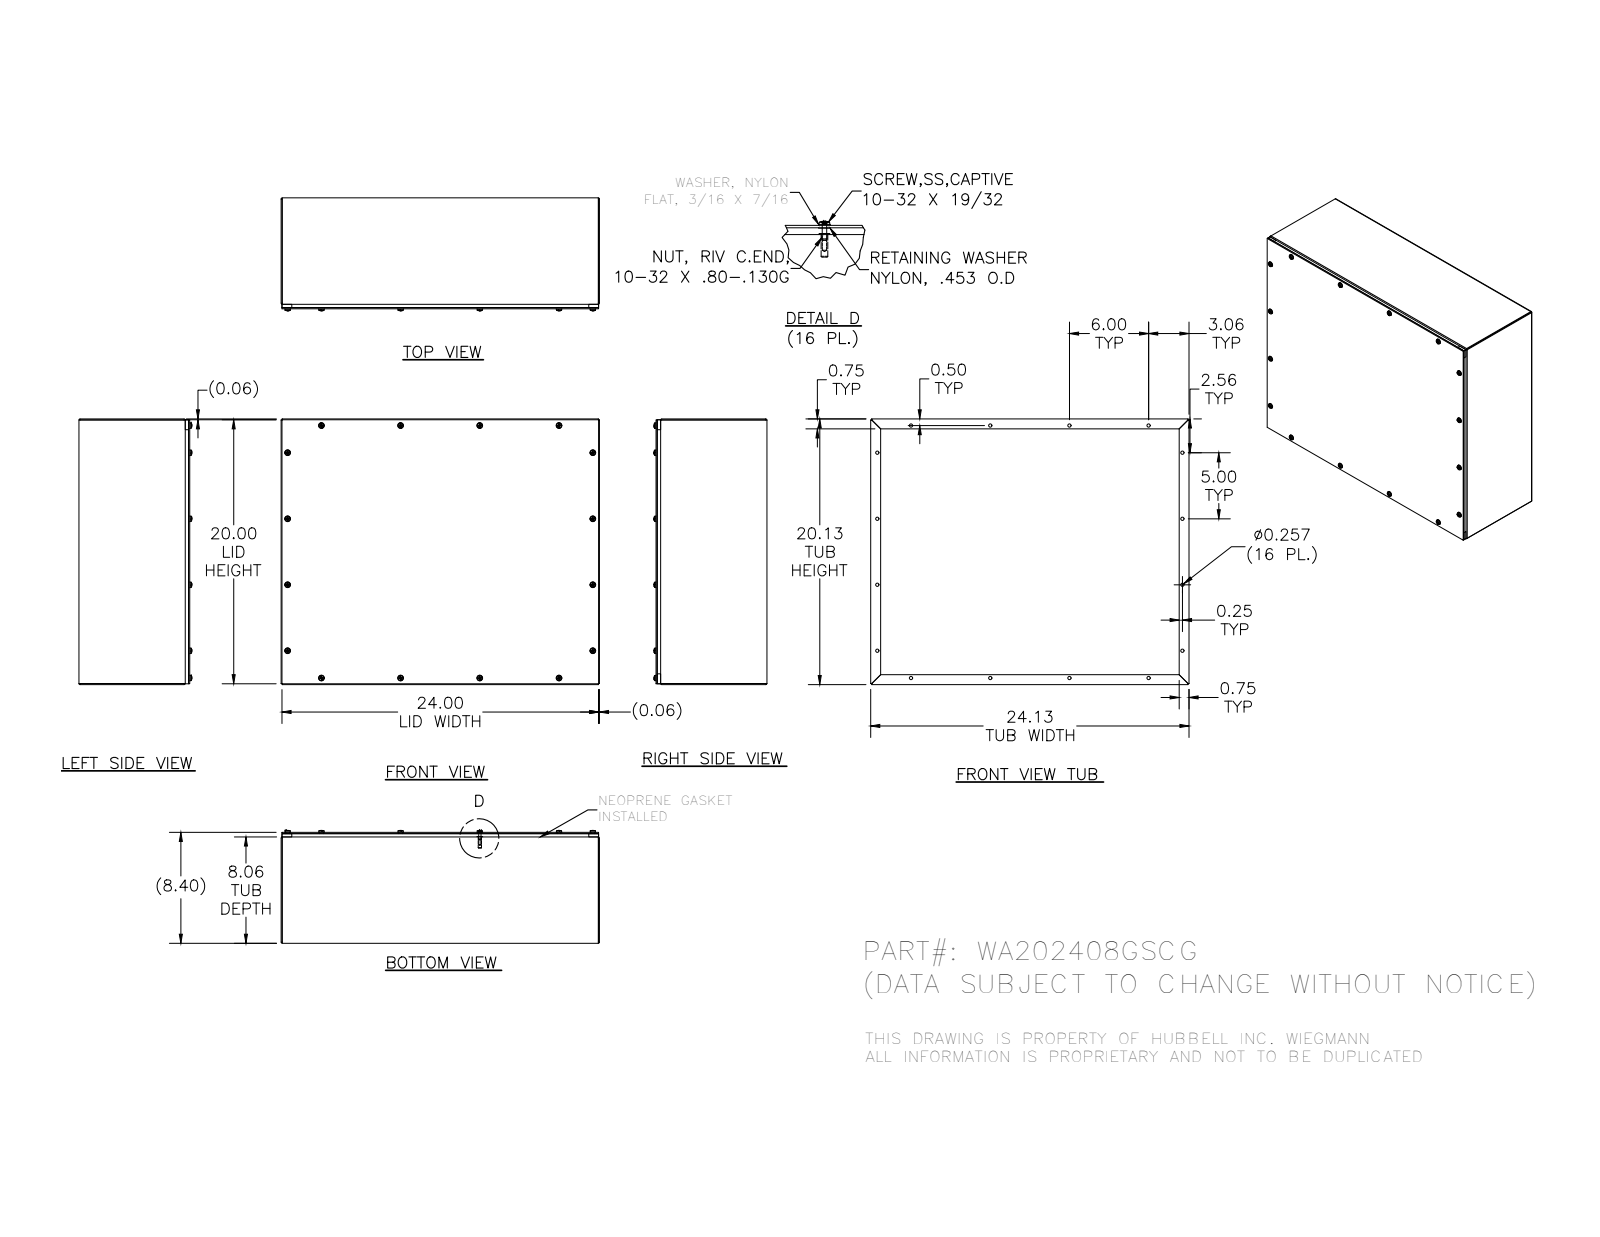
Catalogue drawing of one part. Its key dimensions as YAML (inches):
part_name: "WA202408GSCG; WA2024GSCGLP; 39035; 37210 (+3 more)"
step_written_by: "SolidWorks 2014 (AUTOMOTIVE_DESIGN)"
units: inches
bodies: {solids: 70, faces: 1652, planar: 772, cylindrical: 432, other: 448}
overall_size: [24.125, 20.125, 8.558]
volume: 154.1
surface_area: 3679
round_holes:
  - {diameter: 0.156, count: 16}
  - {diameter: 0.188, count: 16}
  - {diameter: 0.196, count: 16}
  - {diameter: 0.257, count: 16}
  - {diameter: 0.278, count: 16}
  - {diameter: 0.281, count: 16}
round_bosses_or_shafts:
  - {diameter: 0.453, count: 16}
  - {diameter: 0.437, count: 16}
  - {diameter: 0.406, count: 16}
  - {diameter: 0.248, count: 16}
  - {diameter: 0.167, count: 16}
partial_cylinders:
  - {radius: 0.089, count: 16}
  - {radius: 0.016, count: 8}
  - {radius: 0.09, count: 8}
face_to_face_distances: [0.074, 0.094, 8.33, 8.404, 8.236, 8.31, 0.074, 20.051, 20.125, 19.977]
hole_center_spacings: [6, 5, 12, 20.044, 23.658, 23.659, 10, 14.707]
